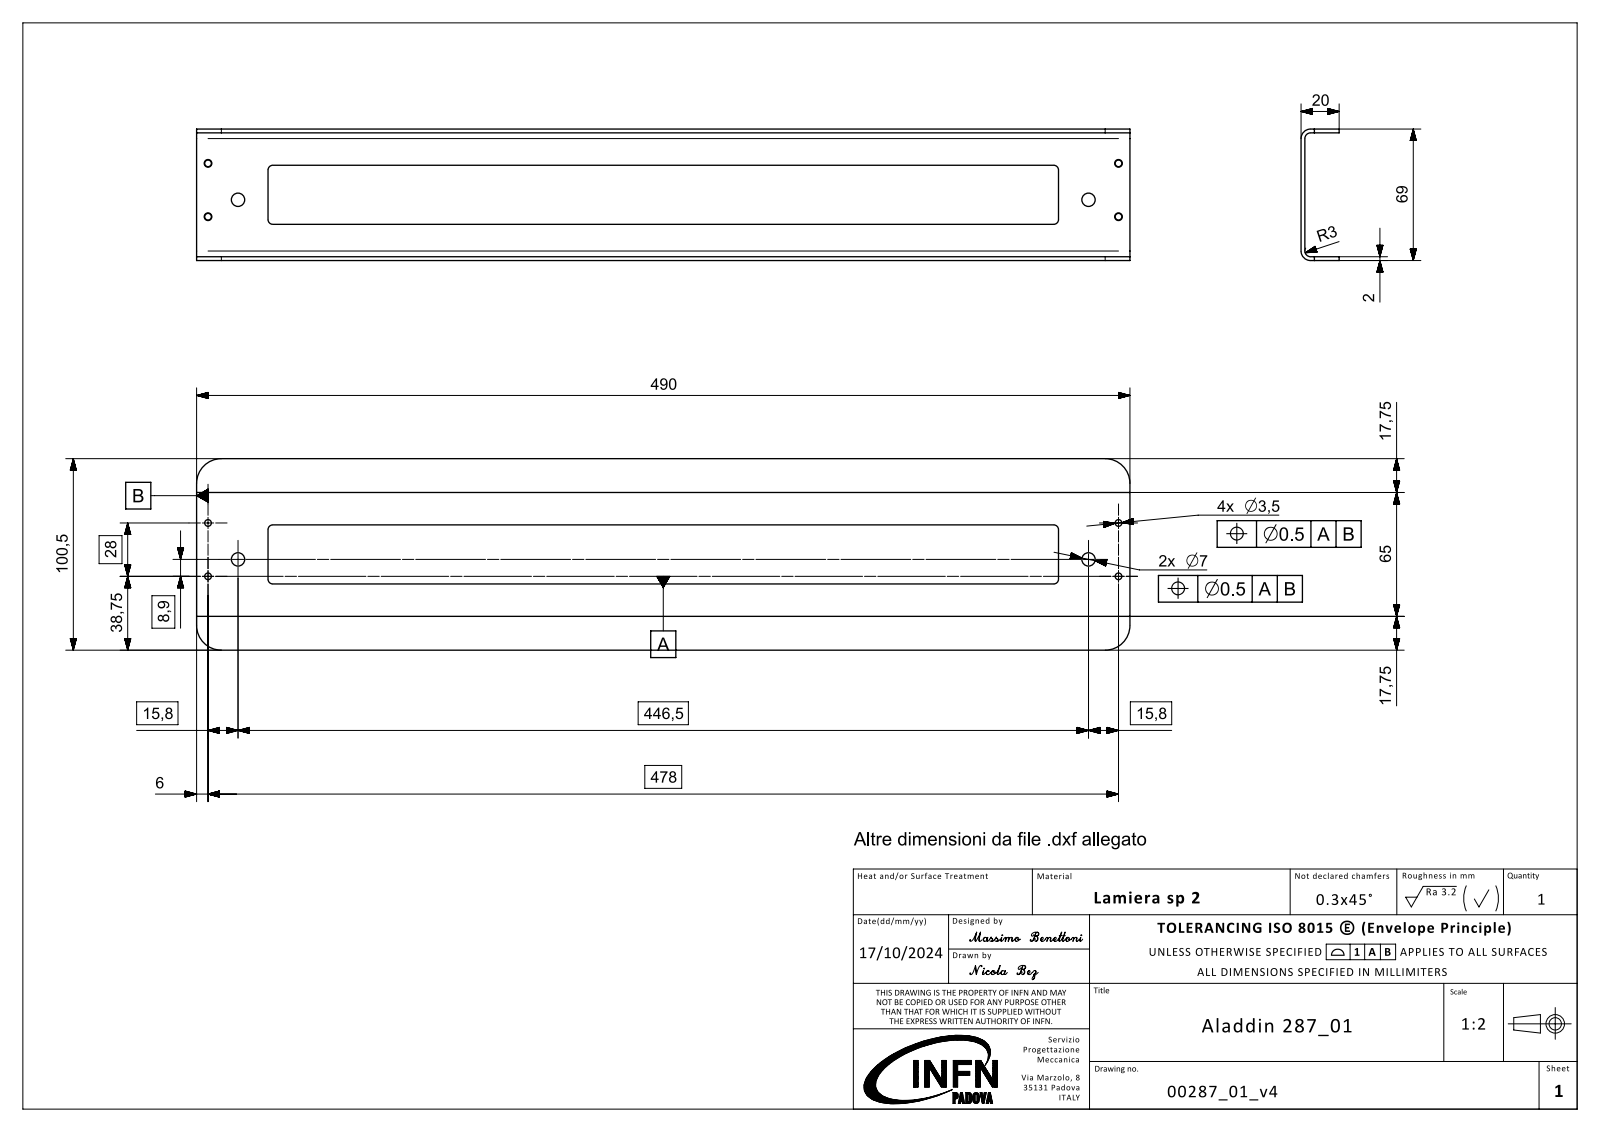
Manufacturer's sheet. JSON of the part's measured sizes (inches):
{"part_name": "00287_01_v4_objects", "step_written_by": "SIEMENS PLM Software NX2306.9102 (AUTOMOTIVE_DESIGN)", "units": "inches", "bodies": {"solids": 1, "faces": 40, "planar": 14, "cylindrical": 18, "other": 8}, "overall_size": [19.291, 2.717, 0.787], "volume_in3": 4.473, "surface_area_in2": 120.2, "round_holes": [[0.138, 4], [0.276, 2]], "partial_cylinders_radius": [[0.098, 4], [0.118, 2], [0.197, 2], [0.512, 2]], "face_to_face_distances": [0.079, 2.638, 2.717, 2.559, 0.709, 0.787, 0.748, 1.969, 0.669, 1.89], "hole_center_spacings": [0.712, 0.975, 1.102, 18.202, 18.214, 18.819, 18.851, 17.579]}
